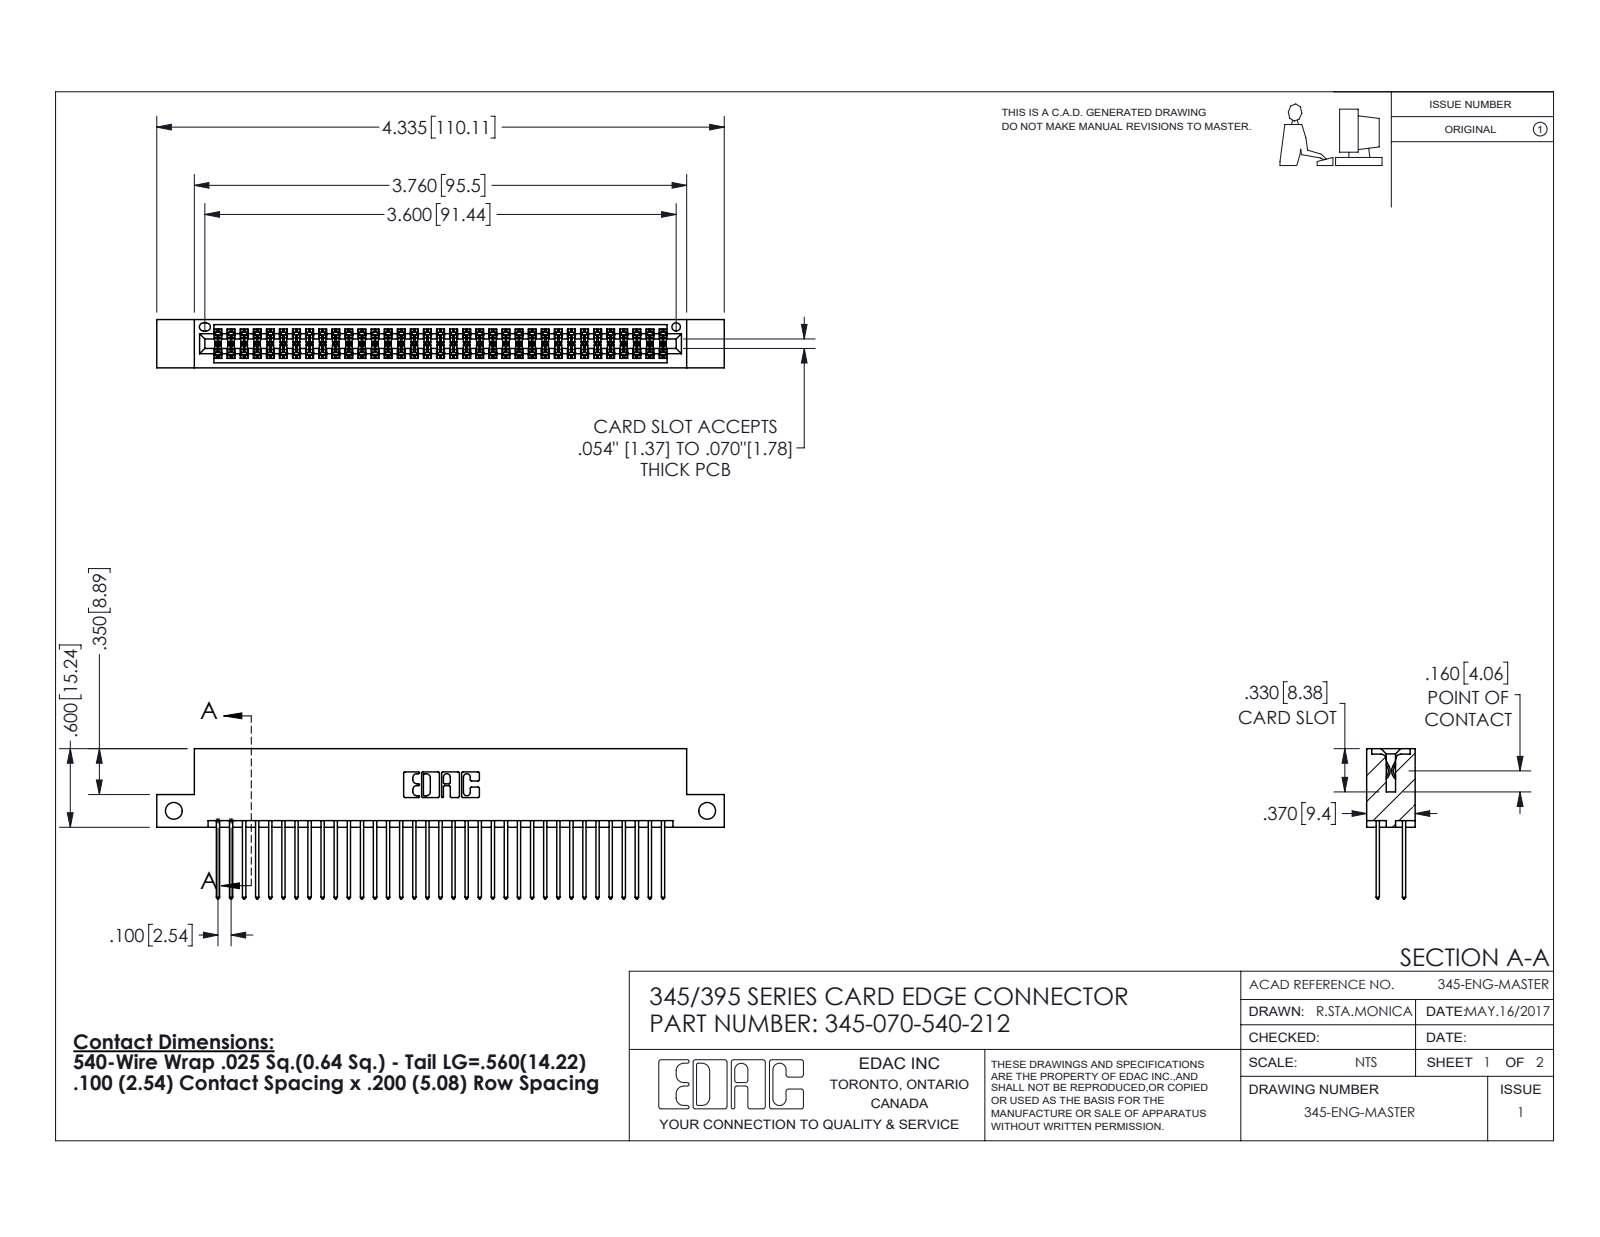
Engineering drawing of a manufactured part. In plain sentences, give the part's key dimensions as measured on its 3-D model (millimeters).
The part is named "345-070-540-212; 345 Part_Flush Mounting Lugs - Side Mount; 345-292-001_345-293-140". Its 3-D file was written by "SolidWorks 2016 (CONFIG_CONTROL_DESIGN)". It is 71 solids with 3626 faces: 2390 planar, 1236 cylindrical and 0 other. Overall it measures 110.1 by 29.1 by 9.4 millimeters. Its volume is 10 800 cubic millimeters and its surface area 16 940 square millimeters. Round holes: 2 of diameter 3.3, 1 of diameter 1.6. Partial cylindrical surfaces (rounded edges, fillets, slot ends): 105 of radius 0.2, 70 of radius 0.3, 22 of radius 0.3, 6 of radius 0.2, 6 of radius 0.8, 3 of radius 0.7, 2 of radius 0.4, 2 of radius 0.5. The main face-to-face distances are 7.6, 1.8, 5.1, 2.5, 6.9, 0.6, 9.4, 5.7, 4.4, 3.8. The hole center spacings are 103.5.
